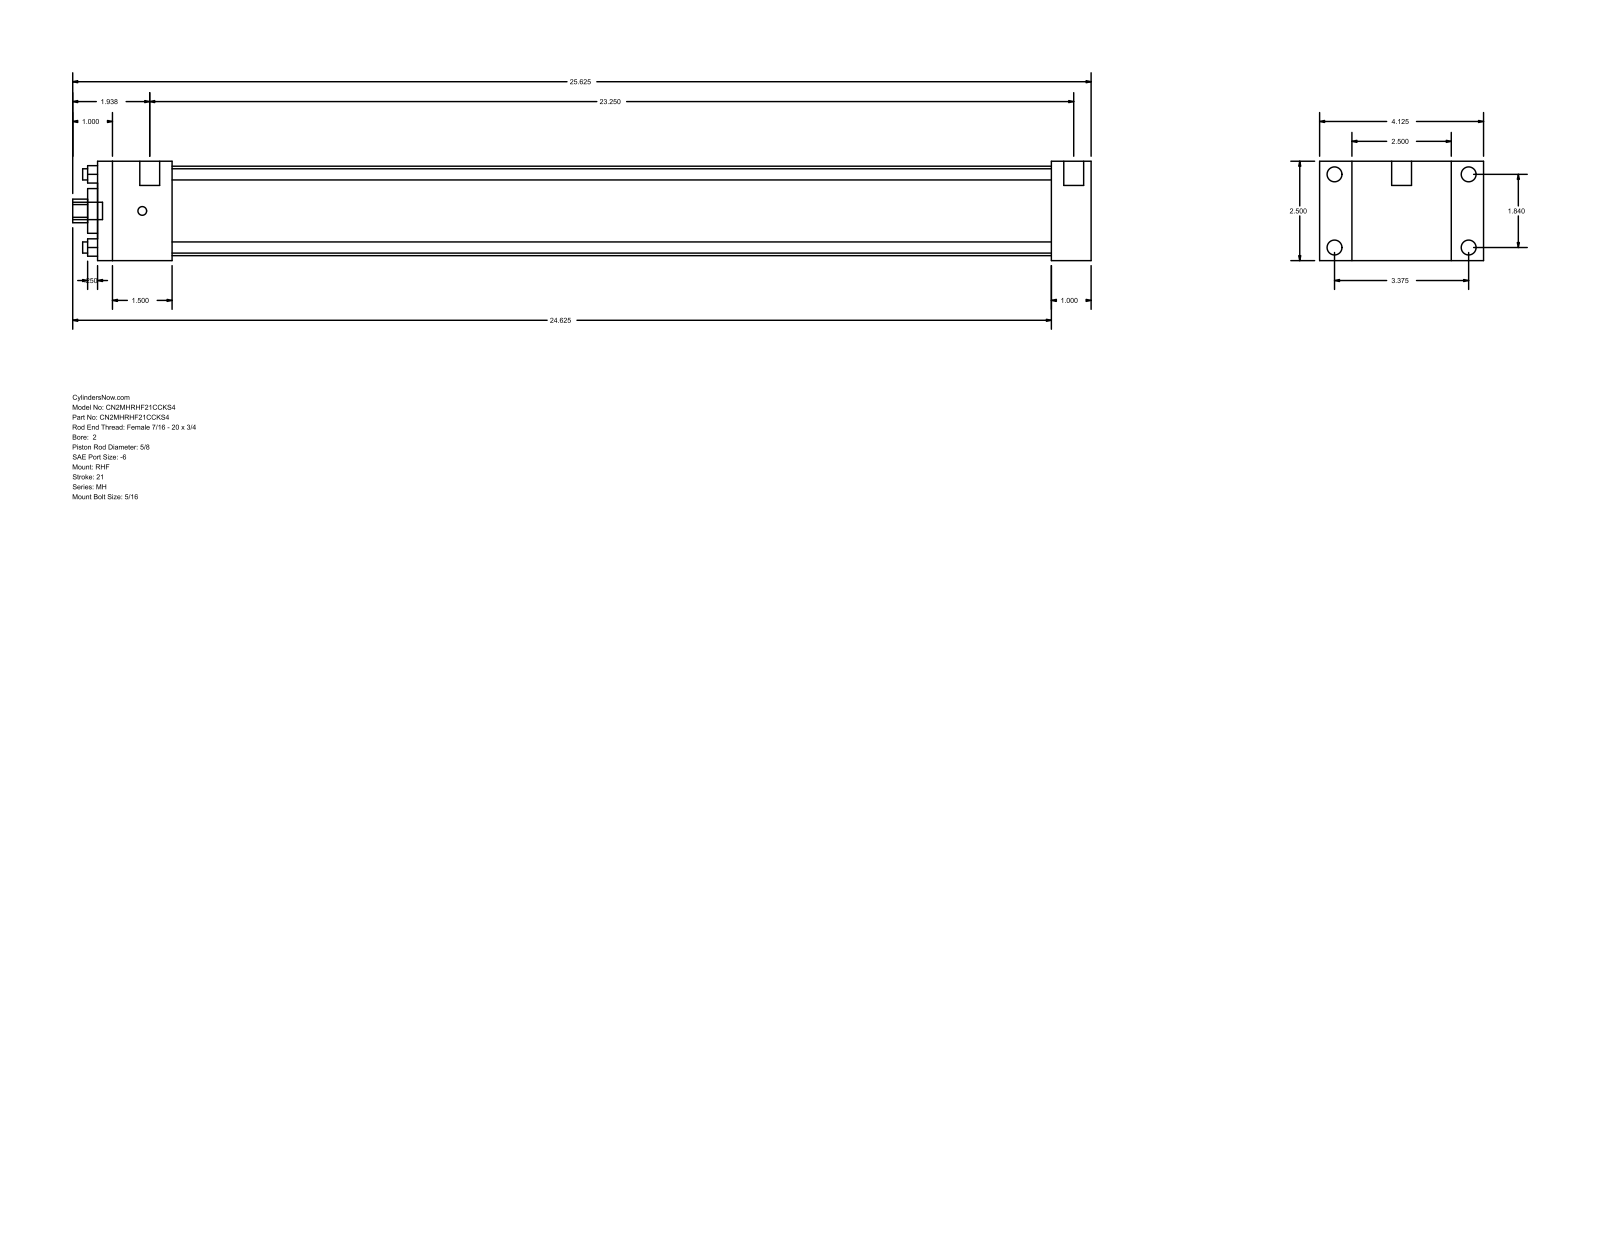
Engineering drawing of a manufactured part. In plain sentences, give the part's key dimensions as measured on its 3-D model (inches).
The part is named "MH_RHF__0200_0.625". Its 3-D file was written by "GSSL Pune (CONFIG_CONTROL_DESIGN)". It is 0 solids with 88 faces: 60 planar, 28 cylindrical and 0 other. Overall it measures 25.625 by 4.125 by 2.5 inches. Round holes: 4 of diameter 0.281, 1 of diameter 0.625, 1 of diameter 1.125, 1 of diameter 2.25. Round bosses or shafts: 4 of diameter 0.375, 4 of diameter 0.219, 2 of diameter 0.5, 1 of diameter 0.437. Partial cylindrical surfaces (rounded edges, fillets, slot ends): 1 of radius 0.297. The main face-to-face distances are 2.5, 1, 0.813, 3.313, 24, 25, 4.125, 1.875, 22.125, 23.125. The hole center spacings are 1.301, 1.84, 2.602.
